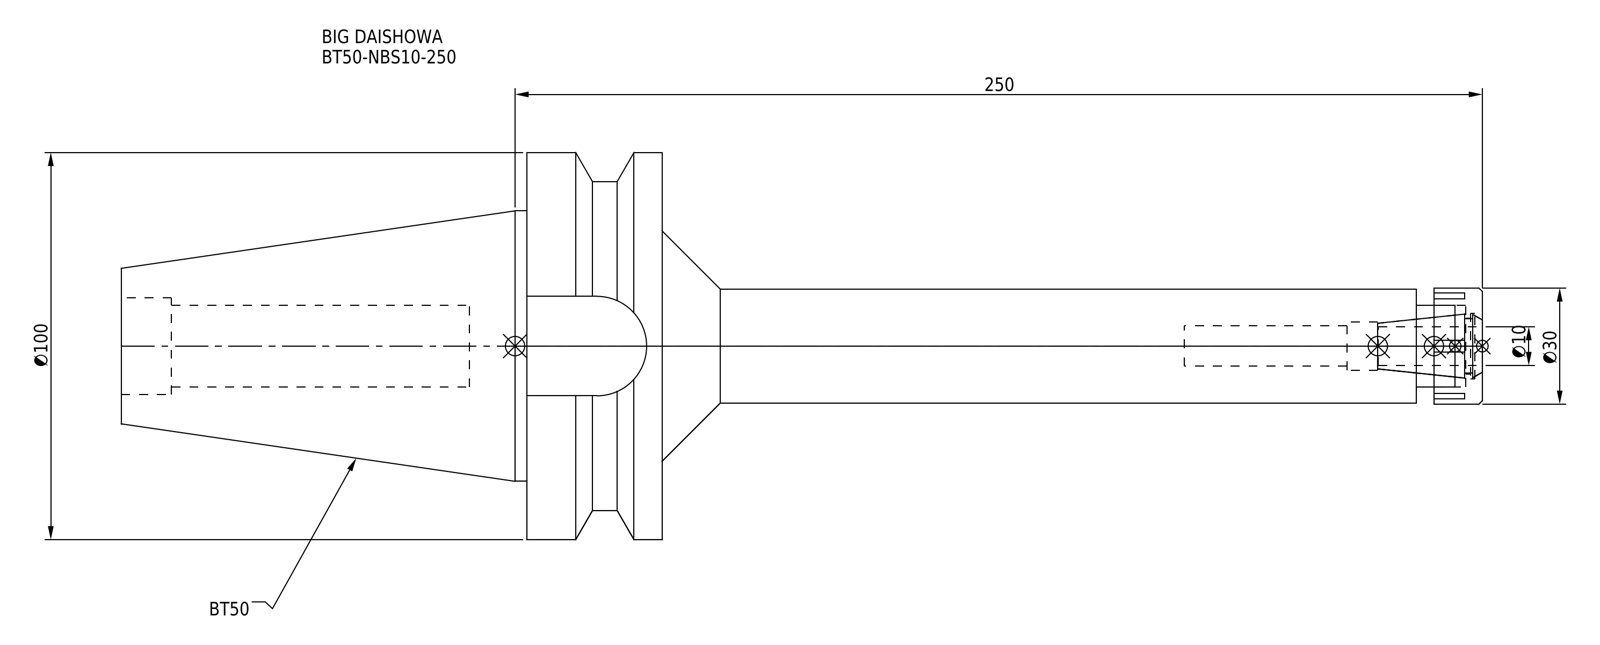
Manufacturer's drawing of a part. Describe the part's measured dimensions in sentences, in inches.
The part is named "BT50-NBS10-250_1.stp; BT50-NBS10-250; DXF_TEMP_ASSY_ASM_4_ASM.stp; BT50NB10250-100_ASM.stp (+3 more)". Its 3-D file was written by "SolidWorks 2019 (CONFIG_CONTROL_DESIGN)". It is 2 solids with 89 faces: 45 planar, 30 cylindrical and 14 other. Overall it measures 13.85 by 3.937 by 3.937 inches. Its volume is 37.13 cubic inches and its surface area 116.7 square inches. Round holes: 1 of diameter 0.409, 1 of diameter 0.492, 1 of diameter 0.571, 1 of diameter 0.669, 1 of diameter 0.827, 1 of diameter 0.835, 1 of diameter 0.984. Round bosses or shafts: 1 of diameter 3.937, 1 of diameter 3.346, 1 of diameter 2.75, 1 of diameter 1.181, 1 of diameter 1.161. Partial cylindrical surfaces (rounded edges, fillets, slot ends): 1 of radius 0.506. The main face-to-face distances are 1.378, 5.504, 4.126, 2.787, 8.346, 9.724, 13.85, 10.307, 1.012, 0.177.
